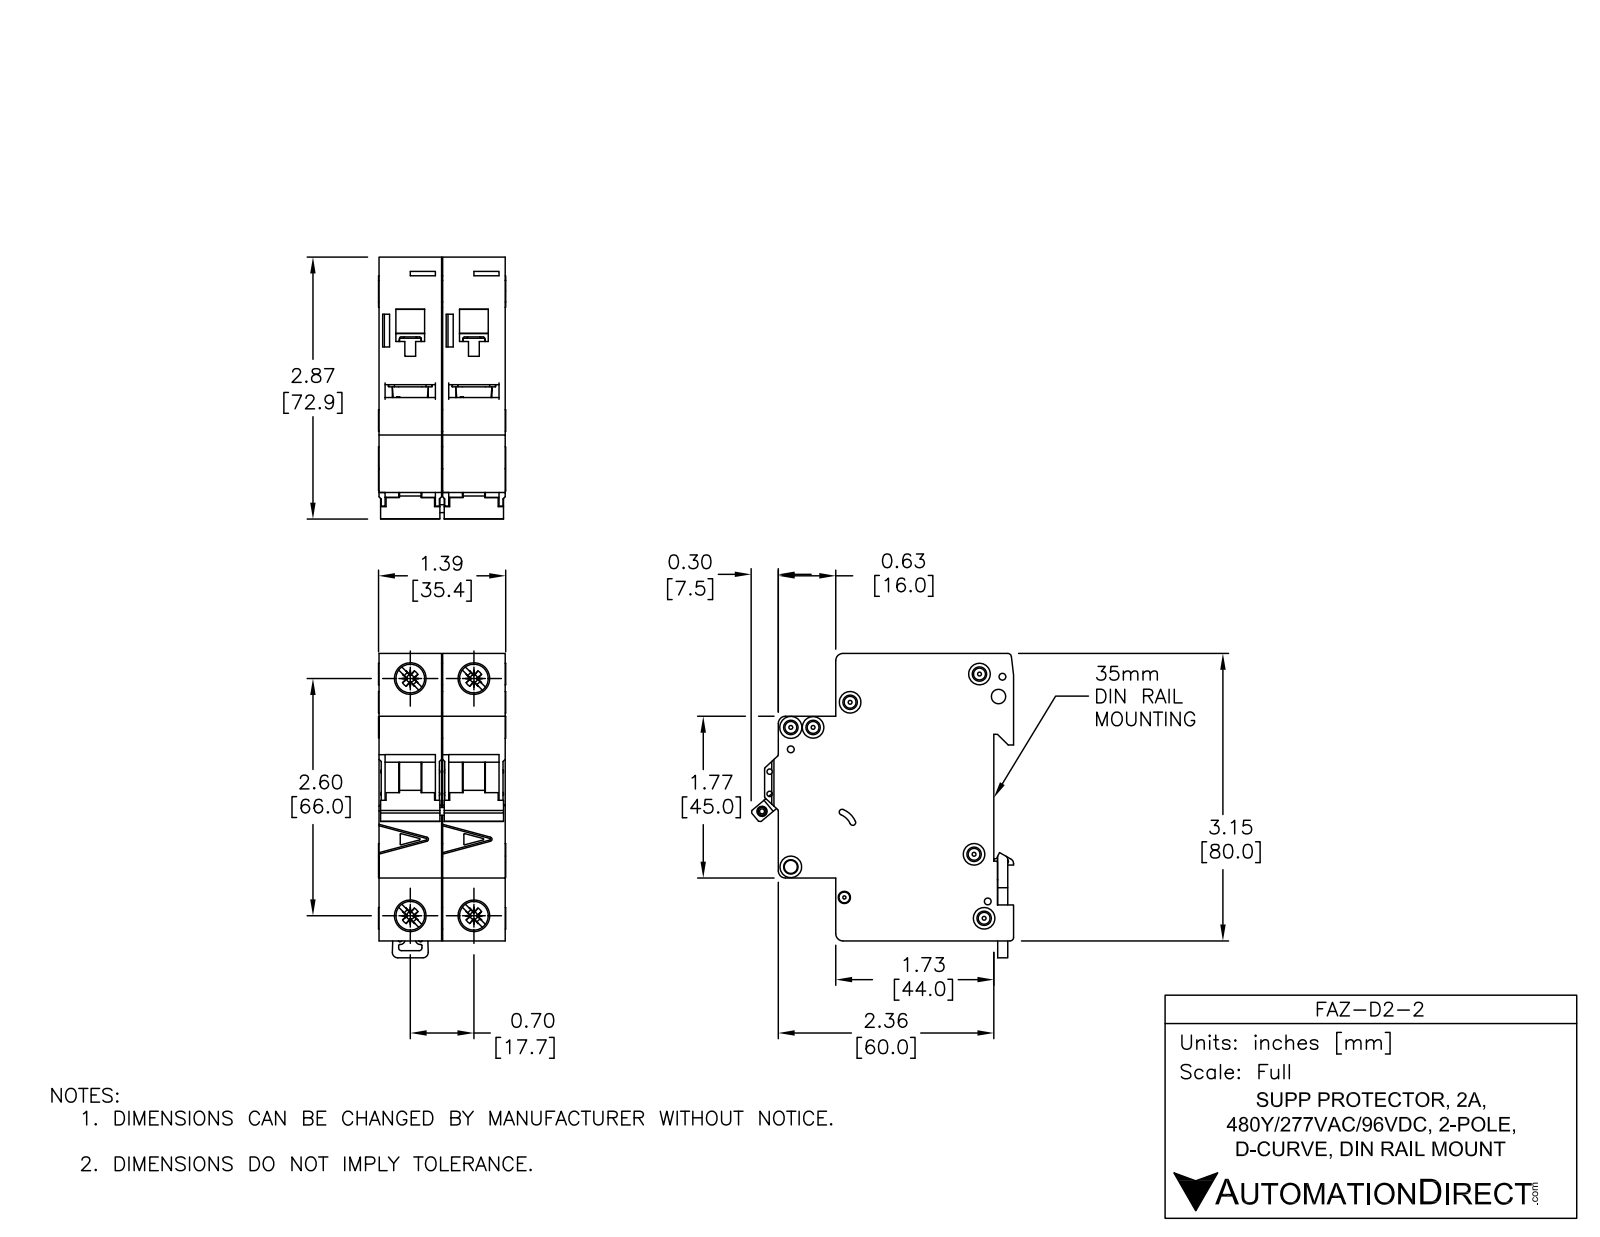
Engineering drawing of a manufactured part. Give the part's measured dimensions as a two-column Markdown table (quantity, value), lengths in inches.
| quantity | value |
| --- | --- |
| part name | FAZ-D2-2 |
| STEP written by | SolidWorks 2014 (AUTOMOTIVE_DESIGN) |
| units | inches |
| bodies | 8 solids, 1104 faces (466 planar, 396 cylindrical, 242 other) |
| overall size | 3.338 × 2.876 × 1.394 |
| volume | 9.142 in³ |
| surface area | 60.14 in² |
| round holes (diameter × count) | 0.142 × 6, 0.075 × 3, 0.043 × 2, 0.059 × 2, 0.157 × 2, 0.281 × 2, 0.323 × 2, 0.085 × 1, 0.087 × 1, 0.1 × 1, 0.13 × 1, 0.134 × 1 |
| round bosses / shafts (diameter × count) | 0.236 × 4, 0.323 × 2, 0.098 × 2 |
| partial cylindrical surfaces (radius × count) | 0.01 × 49, 0.02 × 19, 0.079 × 10, 0.008 × 8, 0.039 × 8, 0.031 × 2, 0.071 × 2, 0.118 × 2 |
| main face-to-face distances | 0.697, 0.689, 1.386, 3.129, 0.217, 1.949, 1.732, 2.579, 2.362, 0.63 |
| hole center spacings | 0.244, 0.537, 0.697, 2.598, 2.69, 0.189, 0.204, 0.221 |
